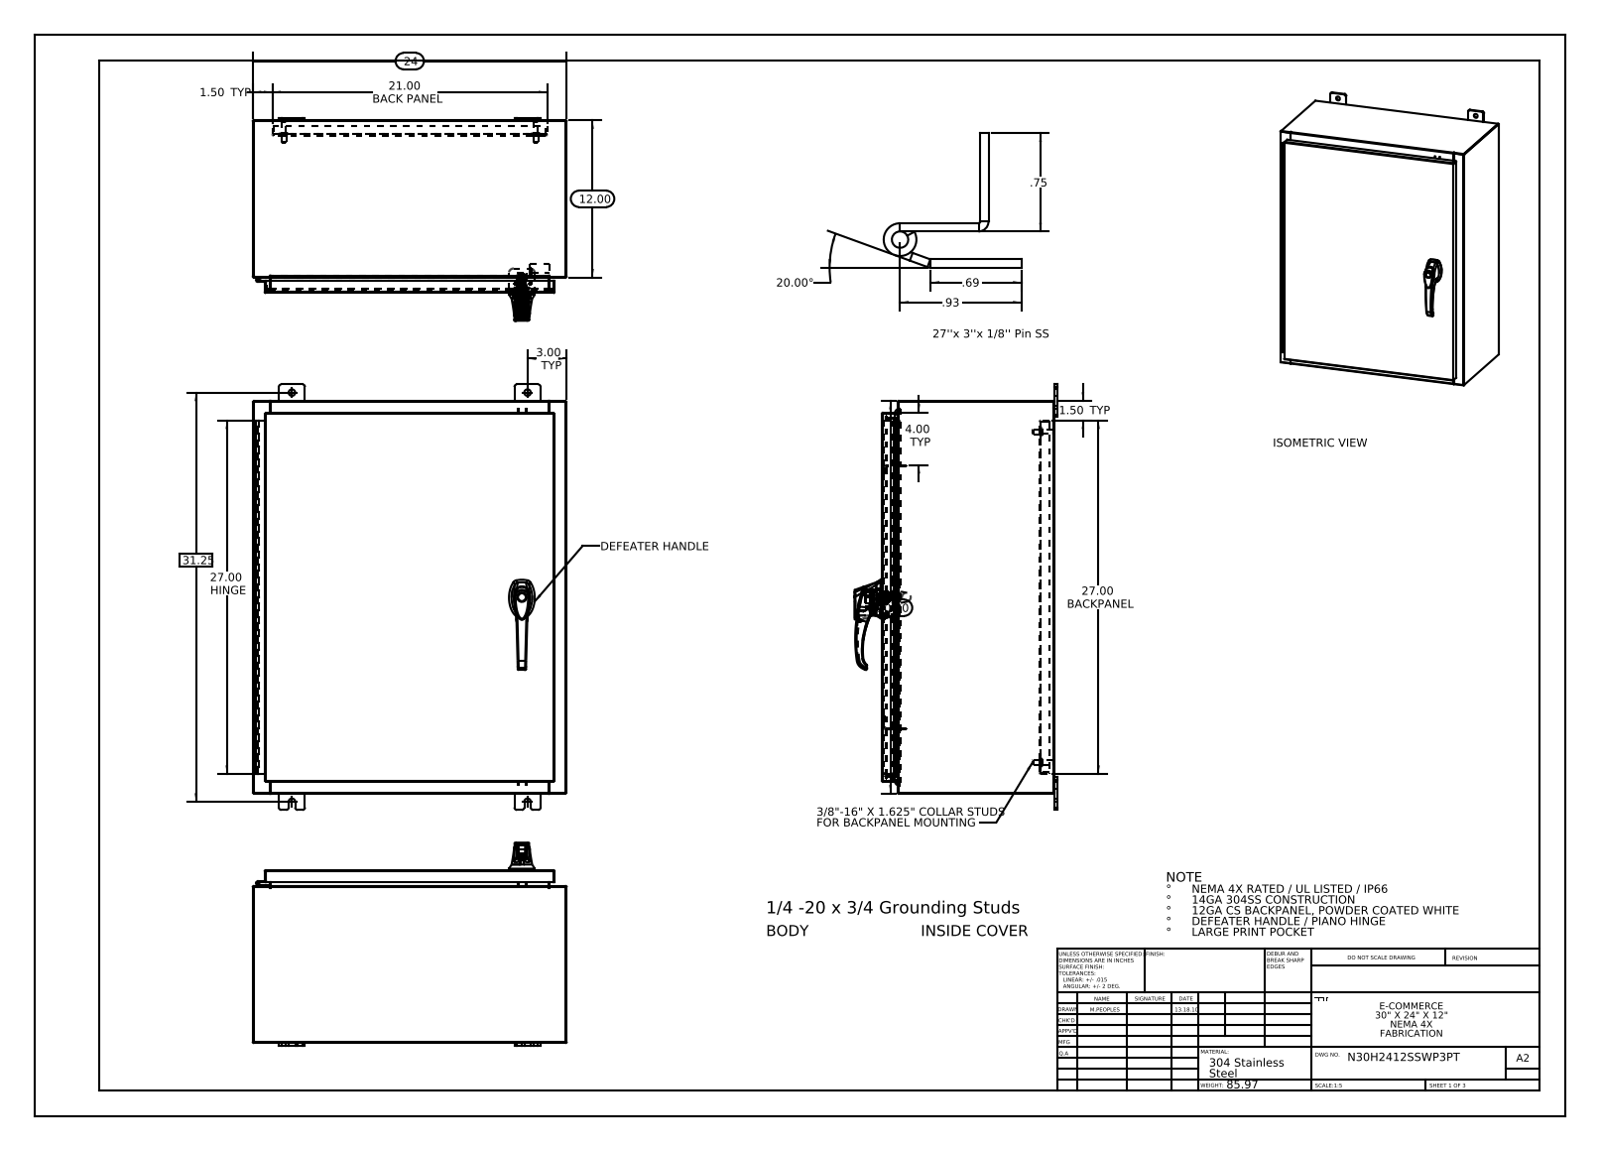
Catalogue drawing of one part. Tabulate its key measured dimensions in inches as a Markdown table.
| quantity | value |
| --- | --- |
| part name | 00005090; 00005310_26163101; 21130102; 022151 (+8 more) |
| STEP written by | SolidWorks 2013 (CONFIG_CONTROL_DESIGN) |
| units | inches |
| bodies | 31 solids, 2576 faces (953 planar, 969 cylindrical, 654 other) |
| overall size | 32.5 × 24 × 15.495 |
| volume | 304.1 in³ |
| surface area | 7 574 in² |
| round holes (diameter × count) | 0.5 × 8, 0.25 × 4, 0.138 × 3, 0.161 × 3, 0.079 × 2, 0.203 × 2, 0.313 × 2, 0.437 × 2, 0.125 × 1, 0.125 × 1, 0.197 × 1, 0.276 × 1 |
| round bosses / shafts (diameter × count) | 0.625 × 4, 0.375 × 4, 0.33 × 4, 1.181 × 1, 0.748 × 1, 0.68 × 1, 0.661 × 1, 0.639 × 1 |
| partial cylindrical surfaces (radius × count) | 0.118 × 37, 0.006 × 33, 0.013 × 24, 0.19 × 24, 0.088 × 18, 0.039 × 15, 0.028 × 12, 0.008 × 6 |
| main face-to-face distances | 0.075, 13.126, 23.925, 0.104, 13.051, 13.201, 1, 29.925, 1.075, 12.051 |
| hole center spacings | 8.369, 0.295, 0.625, 0.841, 1.25, 1.313, 1.561, 1.858 |
